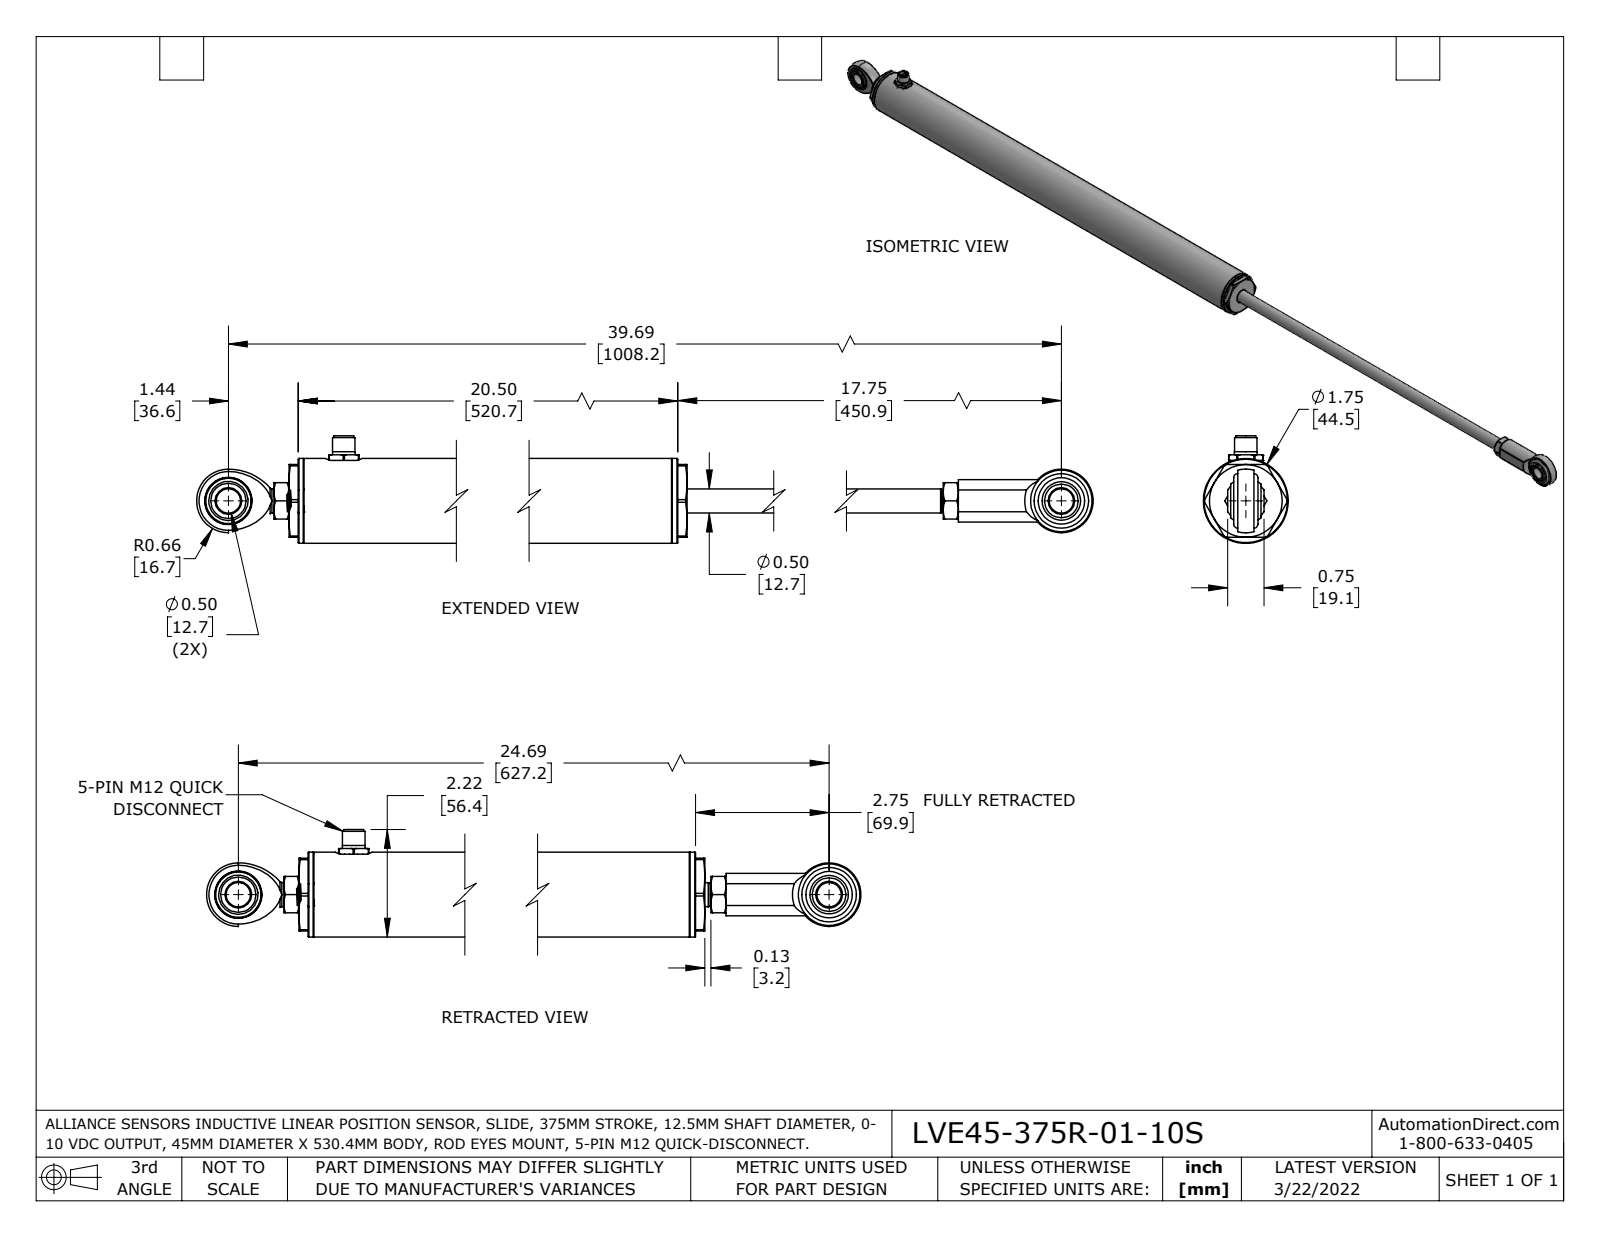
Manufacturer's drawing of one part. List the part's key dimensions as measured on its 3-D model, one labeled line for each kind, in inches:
Part name (STEP PRODUCT): 5500-0013, PCB (Dia .685)_MHPE; 3100-0041-XX-Z_3100-0041-15-Z; 3100-0011-YY; 3100-0212 (+8 more)
STEP written by: SolidWorks 2021 (AUTOMOTIVE_DESIGN)
Units: inches
Bodies: 23 solids, 873 faces (198 planar, 297 cylindrical, 378 other)
Overall size (bounding box): 41.004 × 2.219 × 1.75
Volume: 22.89 in³ · Surface area: 351.7 in²
Round holes (diameter × count): ⌀0.501 ×3, ⌀0.197 ×1, ⌀0.25 ×1, ⌀0.264 ×1, ⌀0.309 ×1, ⌀0.329 ×1, ⌀0.339 ×1, ⌀0.413 ×1, ⌀0.417 ×1, ⌀0.453 ×1, ⌀0.478 ×1, ⌀0.5 ×1
Round bosses / shafts (diameter × count): ⌀0.031 ×5, ⌀1.75 ×1, ⌀1.625 ×1, ⌀1.562 ×1, ⌀1.531 ×1, ⌀1.5 ×1, ⌀1.47 ×1, ⌀1.384 ×1
Partial cylindrical surfaces — rounded edges, fillets, slot ends (radius × count): R0.325 ×1, R0.354 ×1, R0.378 ×1, R0.38 ×1, R0.438 ×1, R0.85 ×1
Main face-to-face distances: 1.93, 0.5, 0.38, 0.69, 2.62, 18.573, 2.24, 1.55, 18.763, 18.073
Hole centre spacings: 0.5, 39.693
